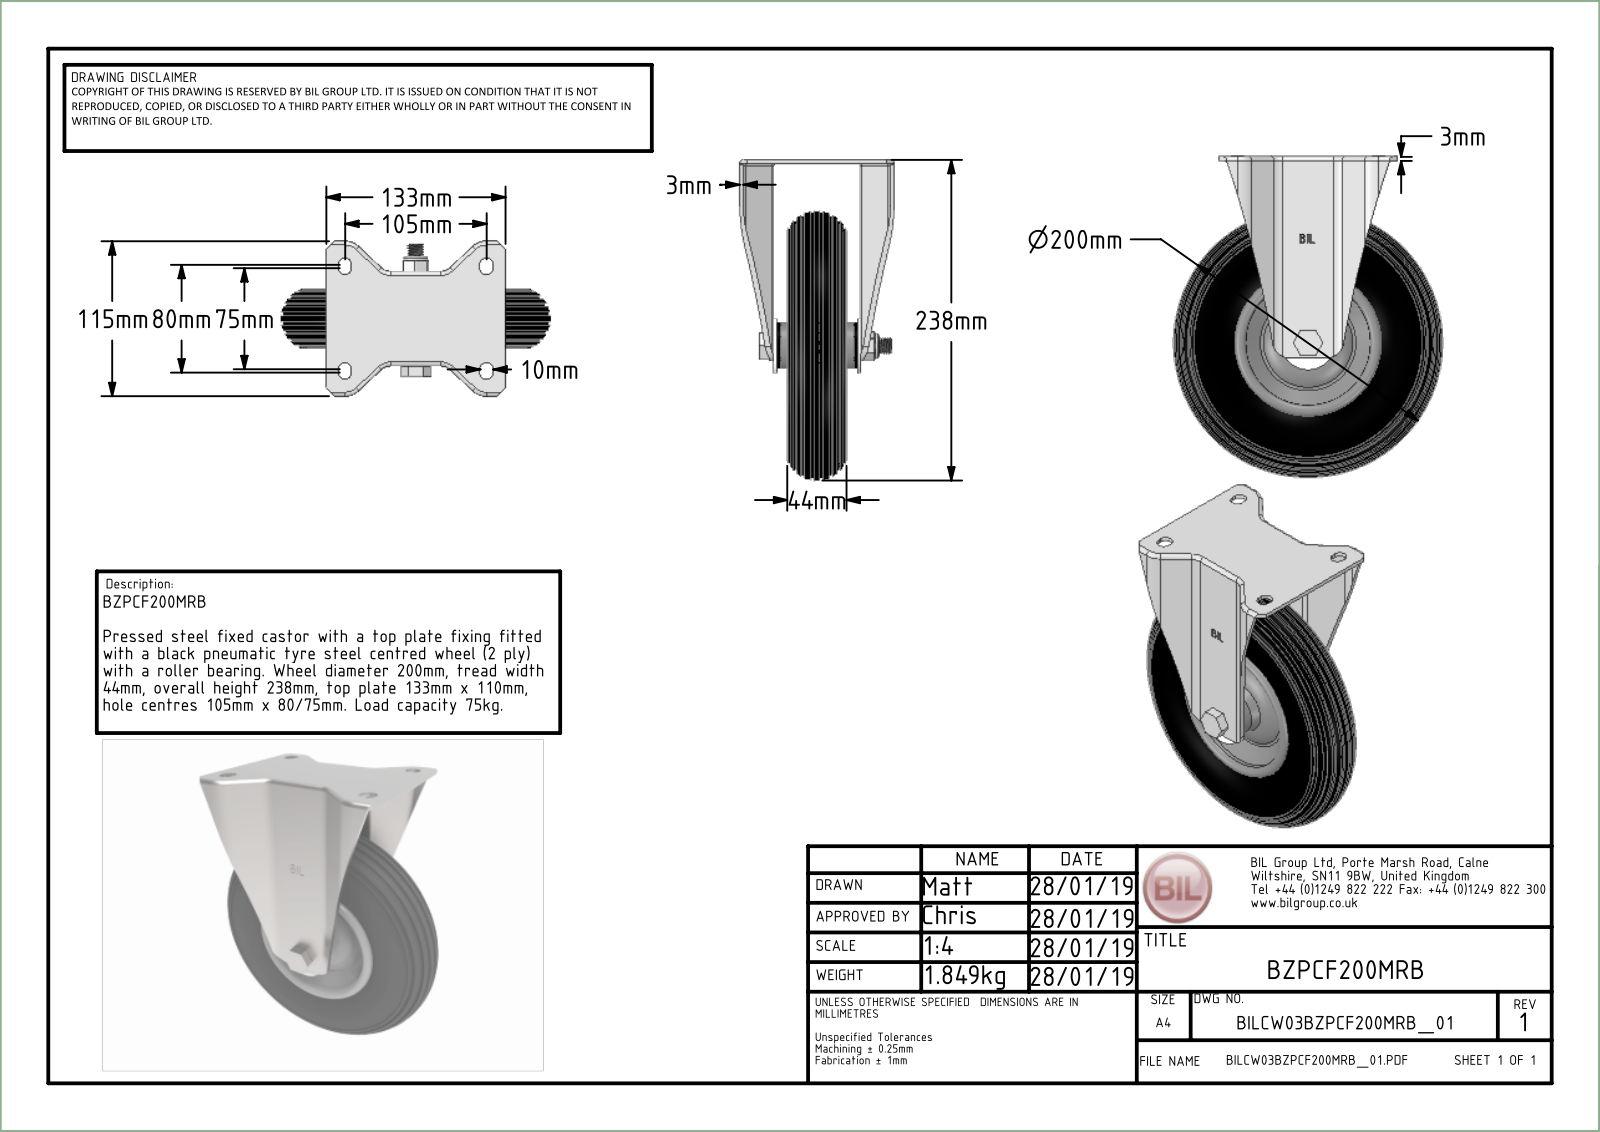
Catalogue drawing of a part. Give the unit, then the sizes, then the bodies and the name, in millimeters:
Units: millimetres
Overall size (bounding box): 238 × 200 × 117
Round holes (diameter × count): ⌀8 ×1, ⌀12 ×1, ⌀12.2 ×1, ⌀12.5 ×1, ⌀14 ×1, ⌀20 ×1, ⌀20.5 ×1, ⌀107 ×1, ⌀150 ×1
Round bosses / shafts (diameter × count): ⌀5 ×10, ⌀7 ×2, ⌀152.01 ×1, ⌀109 ×1, ⌀37.5 ×1, ⌀33.5 ×1, ⌀30 ×1, ⌀29.5 ×1
Partial cylindrical surfaces — rounded edges, fillets, slot ends (radius × count): R0.5 ×18, R3 ×14, R1.5 ×11, R5.5 ×8, R10 ×8, R8 ×6, R0.47 ×4, R0.9 ×4
Main face-to-face distances: 3, 64, 6.22, 61, 67, 9.22, 3.22, 4, 2.5, 1
Volume: 1 111 000 mm³ · Surface area: 377 900 mm²
Bodies: 23 solids, 1057 faces (251 planar, 207 cylindrical, 599 other)
Part name (STEP PRODUCT): BZPCF200MRB v3; BZWBF200AS v1; BZWBF200AS; ZINC PLATED, PRESSED STEEL BRACKET (+8 more)
STEP written by: Autodesk Translation Framework v14.10.0.0 (AUTOMOTIVE_DESIGN)
